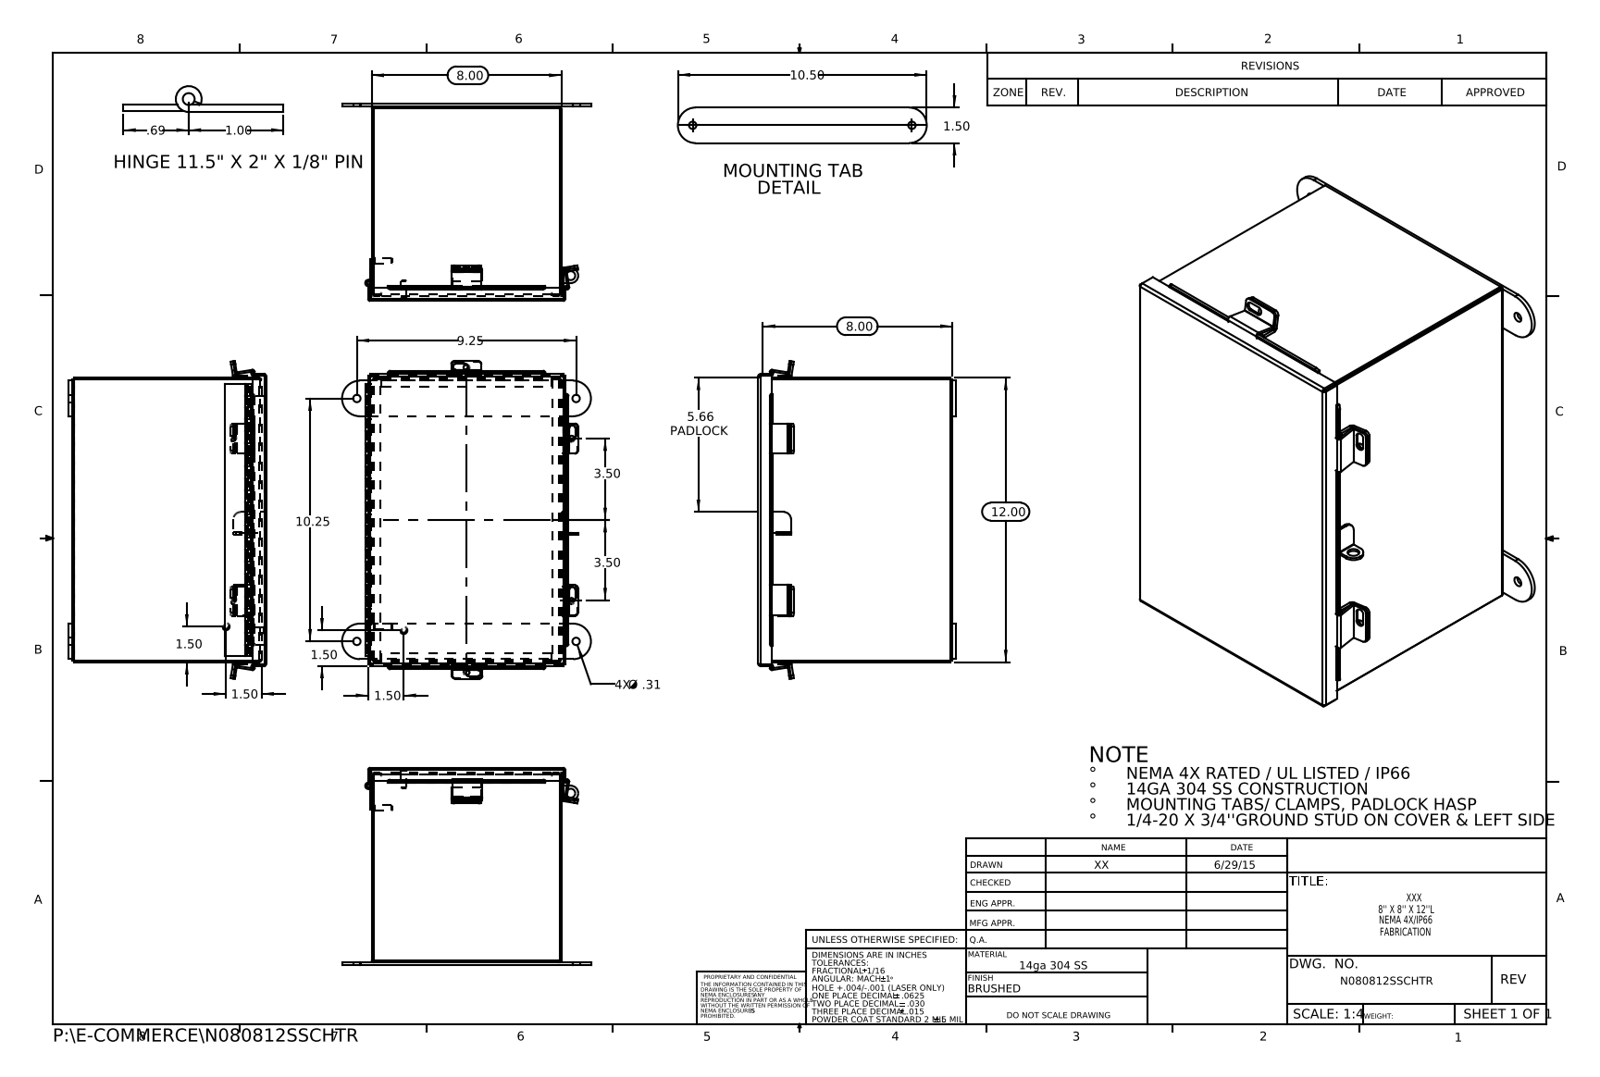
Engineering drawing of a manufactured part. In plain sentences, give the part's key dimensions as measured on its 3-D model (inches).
The part is named "N080812SSCHTR JIC Top; N080812SSCHTR JIC Bottom; N080812SSCHTR JIC Enclosure Template; N080812SSCHTR HW-CD-S-25020-034 (+8 more)". Its 3-D file was written by "SolidWorks 2015 (CONFIG_CONTROL_DESIGN)". It is 19 solids with 624 faces: 393 planar, 211 cylindrical and 20 other. Overall it measures 13.407 by 10.5 by 8.337 inches. Its volume is 47.44 cubic inches and its surface area 1 251 square inches. Round holes: 4 of diameter 0.25, 4 of diameter 0.313, 1 of diameter 0.125, 1 of diameter 0.375. Round bosses or shafts: 2 of diameter 0.315, 2 of diameter 0.236, 1 of diameter 0.273, 1 of diameter 0.25. Partial cylindrical surfaces (rounded edges, fillets, slot ends): 14 of radius 0.125, 12 of radius 0.009, 11 of radius 0.013, 11 of radius 0.088, 8 of radius 0.133, 6 of radius 0.083, 6 of radius 0.1, 4 of radius 0.75. The main face-to-face distances are 0.075, 7.925, 8.128, 11.925, 7.85, 8, 8.203, 8.053, 11.85, 12. The hole center spacings are 9.25, 10.25, 13.807, 6.85, 8.541.
